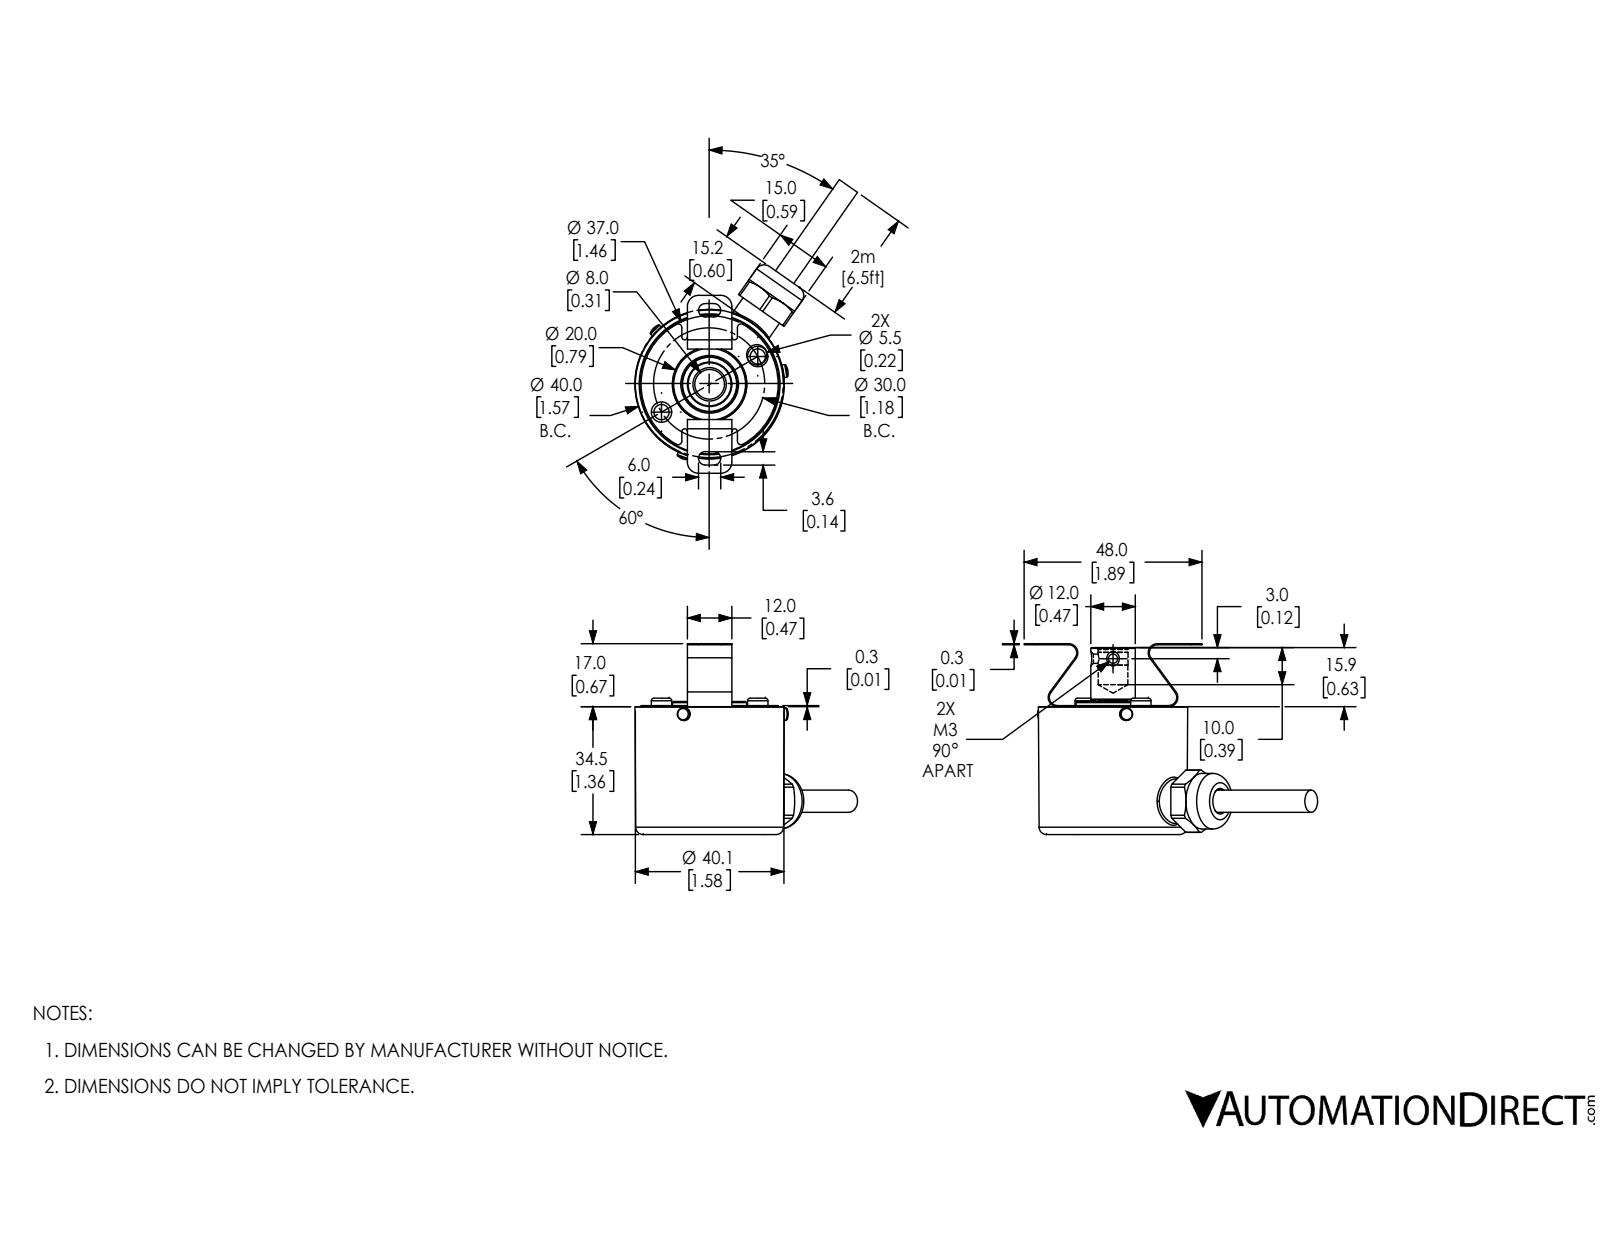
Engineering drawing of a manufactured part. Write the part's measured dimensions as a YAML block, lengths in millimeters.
part_name: "TRD-SHR100AW0D"
step_written_by: "SolidWorks 2017 (AUTOMOTIVE_DESIGN)"
units: millimeters
bodies: {solids: 1, faces: 225, planar: 45, cylindrical: 105, other: 75}
overall_size: [127.58, 67.58, 51.5]
volume: 49859
surface_area: 13138
round_holes:
  - {diameter: 2.2, count: 2}
  - {diameter: 2.5, count: 2}
  - {diameter: 6.5, count: 1}
  - {diameter: 6.6, count: 1}
  - {diameter: 8, count: 1}
  - {diameter: 8.1, count: 1}
  - {diameter: 9, count: 1}
  - {diameter: 11, count: 1}
  - {diameter: 12.2, count: 1}
  - {diameter: 20.1, count: 1}
round_bosses_or_shafts:
  - {diameter: 15, count: 2}
  - {diameter: 12, count: 2}
  - {diameter: 6, count: 2}
  - {diameter: 5.5, count: 2}
  - {diameter: 2, count: 2}
  - {diameter: 37.55, count: 1}
  - {diameter: 20, count: 1}
  - {diameter: 7.6, count: 1}
partial_cylinders:
  - {radius: 0.75, count: 4}
  - {radius: 1, count: 4}
  - {radius: 1.8, count: 4}
  - {radius: 2.2, count: 4}
  - {radius: 2.5, count: 4}
  - {radius: 3, count: 4}
  - {radius: 8.4, count: 1}
  - {radius: 18.2, count: 1}
face_to_face_distances: [34.8, 16.7, 34.5, 16.4, 51.2, 17, 51.5, 15.66, 15.36, 1.04]
hole_center_spacings: [14.94]
